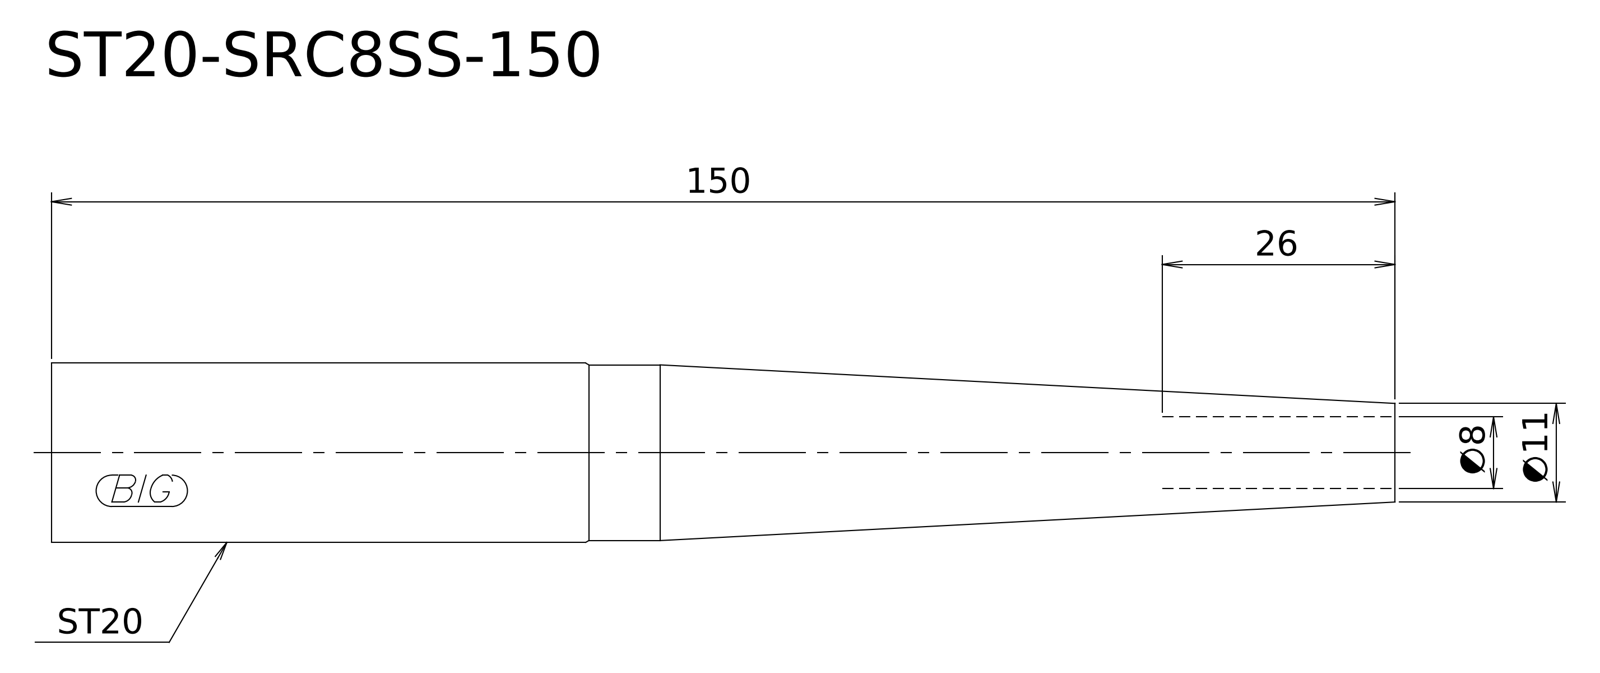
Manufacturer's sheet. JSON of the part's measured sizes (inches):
{"step_written_by": "Kubotek KeyCreator V8.5.1 (14335) (CONFIG_CONTROL_DESIGN)", "units": "inches", "bodies": {"solids": 1, "faces": 6, "planar": 2, "cylindrical": 2, "other": 2}, "overall_size": [5.906, 0.787, 0.787], "volume_in3": 2.241, "surface_area_in2": 13.36, "round_bosses_or_shafts": [[0.787, 1], [0.772, 1]], "face_to_face_distances": [5.906]}
